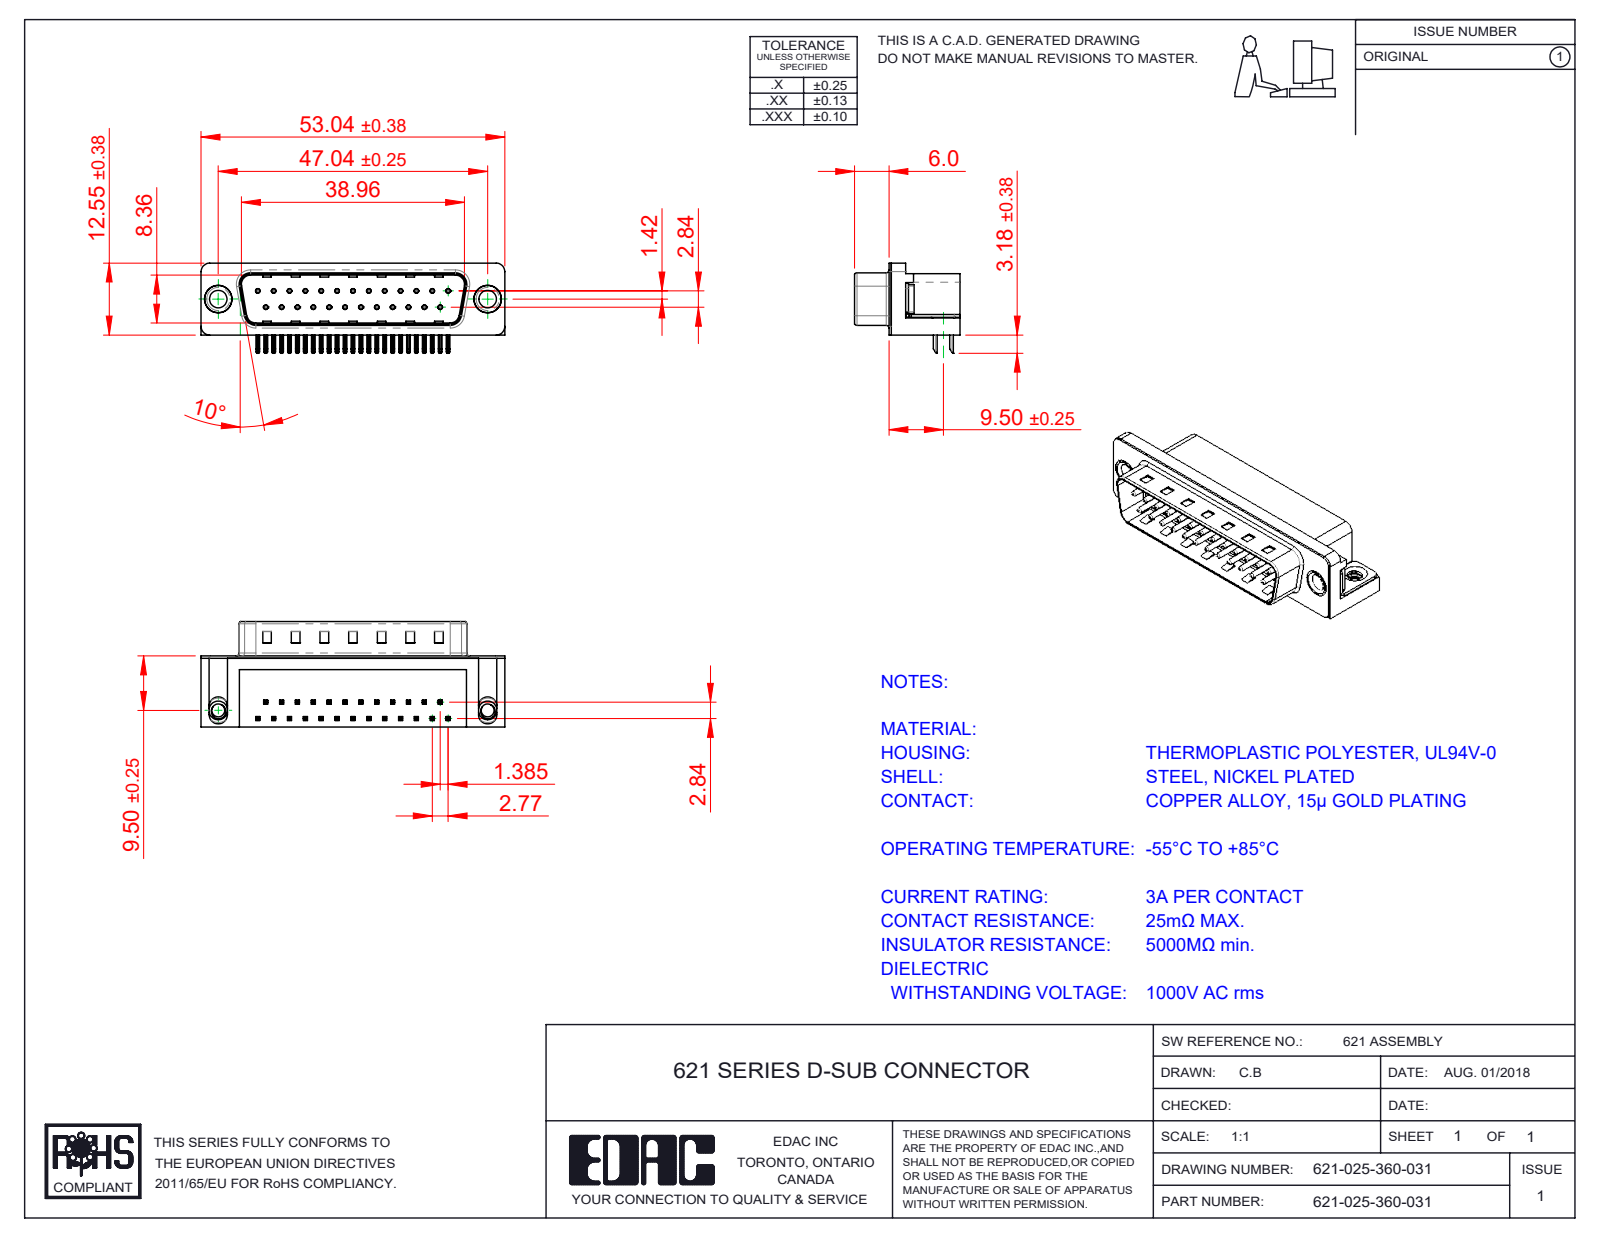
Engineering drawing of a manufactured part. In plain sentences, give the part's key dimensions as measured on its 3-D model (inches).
The part is named "621 Contact Bottom; 621 2 Prong Board Lock; 621-025-360-031; 621 Housing_25 Socket (+3 more)". Its 3-D file was written by "SolidWorks 2016 (CONFIG_CONTROL_DESIGN)". It is 31 solids with 2263 faces: 1437 planar, 649 cylindrical and 177 other. Overall it measures 2.088 by 0.724 by 0.64 inches. Its volume is 0.387 cubic inches and its surface area 11.88 square inches. Round holes: 25 of diameter 0.014, 25 of diameter 0.031, 2 of diameter 0.12, 2 of diameter 0.157, 2 of diameter 0.189, 2 of diameter 0.197. Round bosses or shafts: 25 of diameter 0.03, 2 of diameter 0.193, 2 of diameter 0.187, 2 of diameter 0.152. Partial cylindrical surfaces (rounded edges, fillets, slot ends): 108 of radius 0.01, 50 of radius 0.005, 16 of radius 0.039, 14 of radius 0.02, 8 of radius 0.063, 7 of radius 0.059, 4 of radius 0.013, 4 of radius 0.035. The main face-to-face distances are 0.016, 0.472, 0.407, 0.083, 0.345, 0.412, 0.428, 0.067, 0.488, 0.354. The hole center spacings are 0.124, 0.109, 0.218, 0.327, 0.436, 0.545, 0.654, 0.198.
